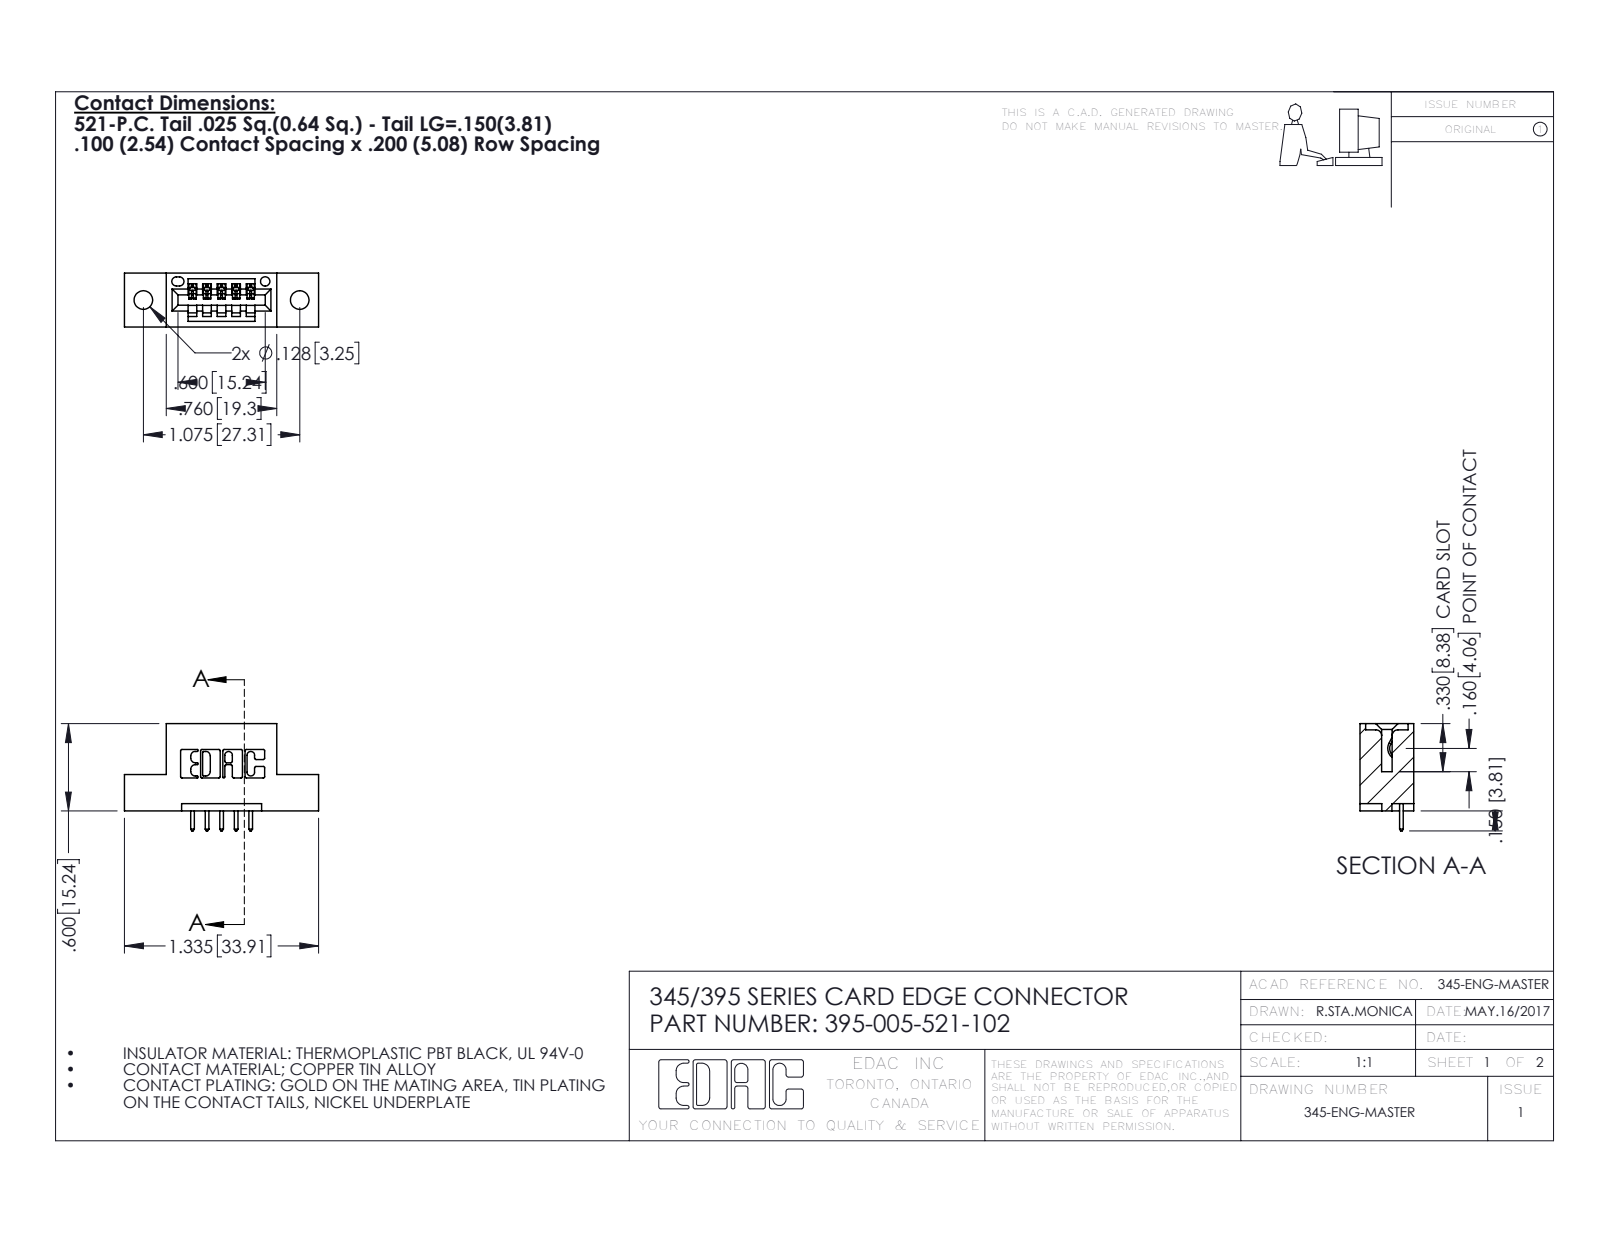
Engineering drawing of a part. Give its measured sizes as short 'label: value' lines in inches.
name: 345 Part_Flush Mounting Lugs - 0.128 Dia; 345-292-001_345-293-121; 395-005-521-102
written by: SolidWorks 2016 (CONFIG_CONTROL_DESIGN)
unit: in
bodies: 6 solids, 416 faces (280 planar, 136 cylindrical, 0 other)
size: 1.335 × 0.737 × 0.37
volume: 0.175 in³; area: 4.618 in²
holes: 2× ⌀0.128, 1× ⌀0.064
rounds: 22× R0.01, 10× R0.006, 10× R0.01, 6× R0.007, 6× R0.031, 3× R0.026, 2× R0.031, 2× R0.04
face distances: 0.2, 0.37, 0.298, 0.072, 0.1, 0.25, 0.025, 0.098, 0.272, 0.06
hole spacings: 0.27, 0.847, 1.075
